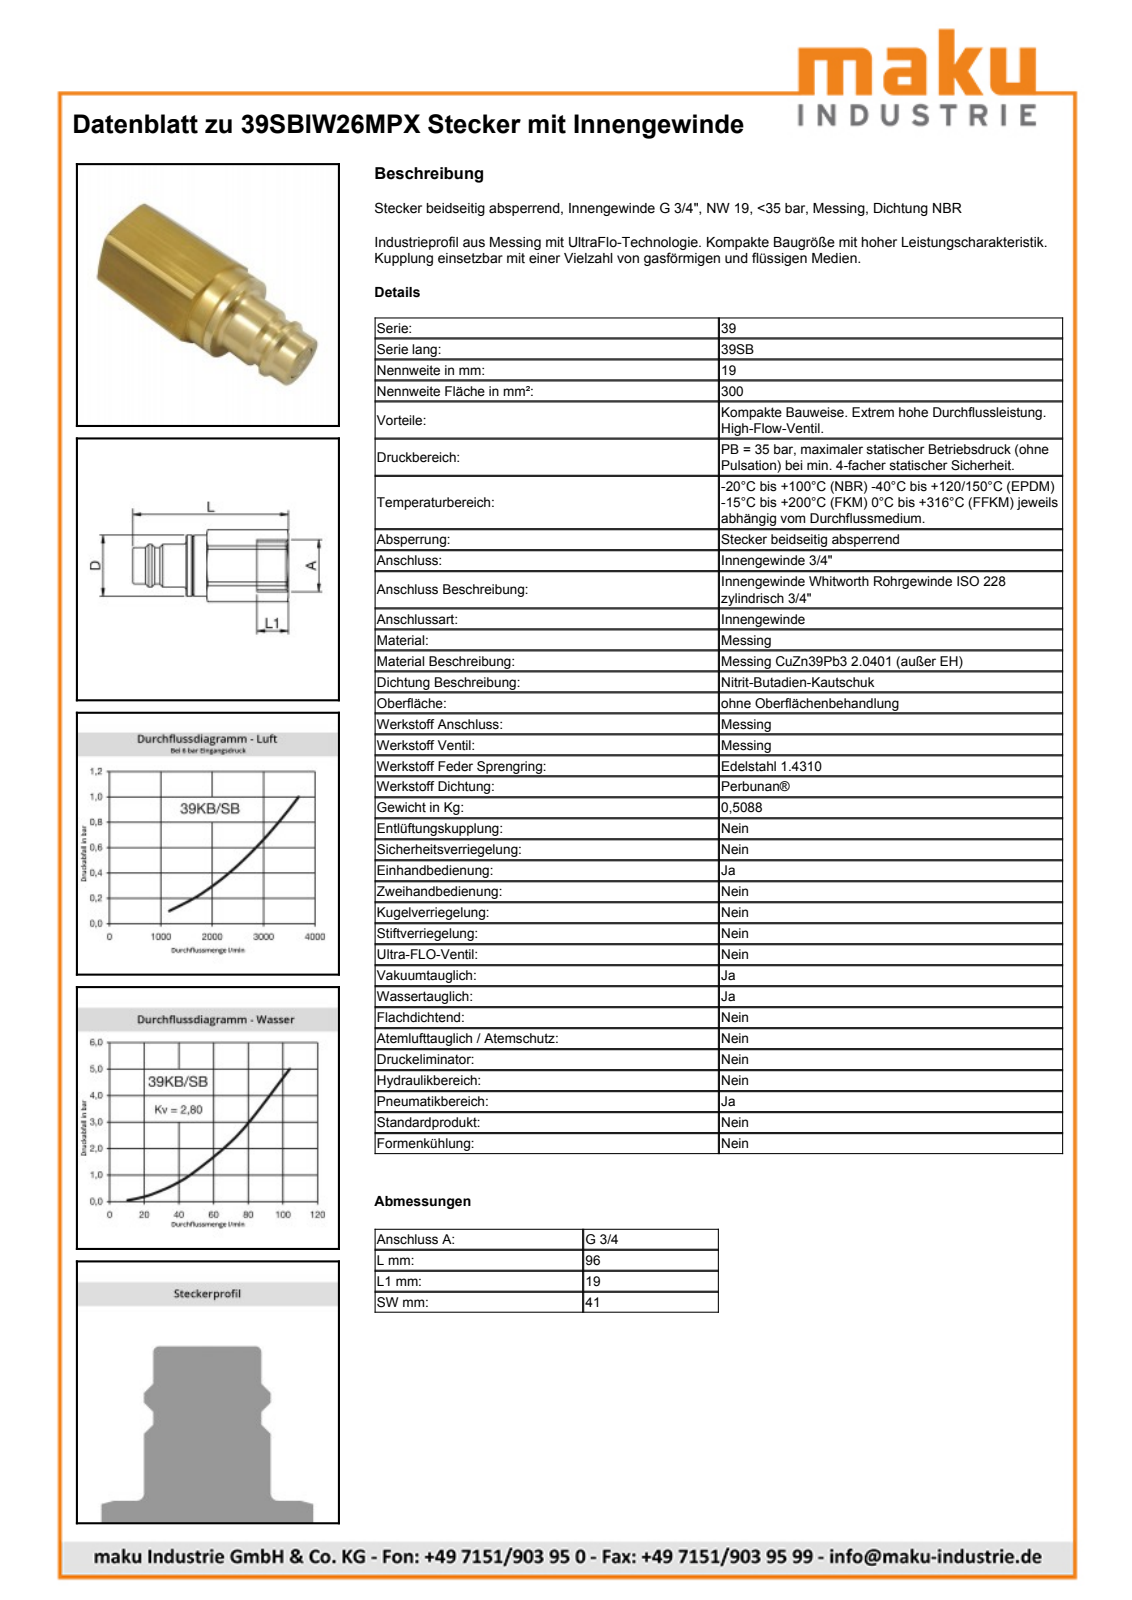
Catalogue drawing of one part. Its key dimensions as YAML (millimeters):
part_name: "D104952"
step_written_by: "Autodesk Inventor 2011 (AUTOMOTIVE_DESIGN)"
units: millimeters
bodies: {solids: 1, faces: 46, planar: 12, cylindrical: 15, other: 19}
overall_size: [98, 45.86, 43.17]
volume: 91588
surface_area: 17213
round_holes:
  - {diameter: 26.44, count: 1}
  - {diameter: 35, count: 1}
round_bosses_or_shafts:
  - {diameter: 39, count: 1}
  - {diameter: 38.8, count: 1}
  - {diameter: 33, count: 1}
  - {diameter: 27.2, count: 1}
  - {diameter: 23.15, count: 1}
partial_cylinders:
  - {radius: 22.98, count: 1}
face_to_face_distances: [41, 27.08, 36.92, 64, 34, 70.92, 98, 38, 4, 32.92]
